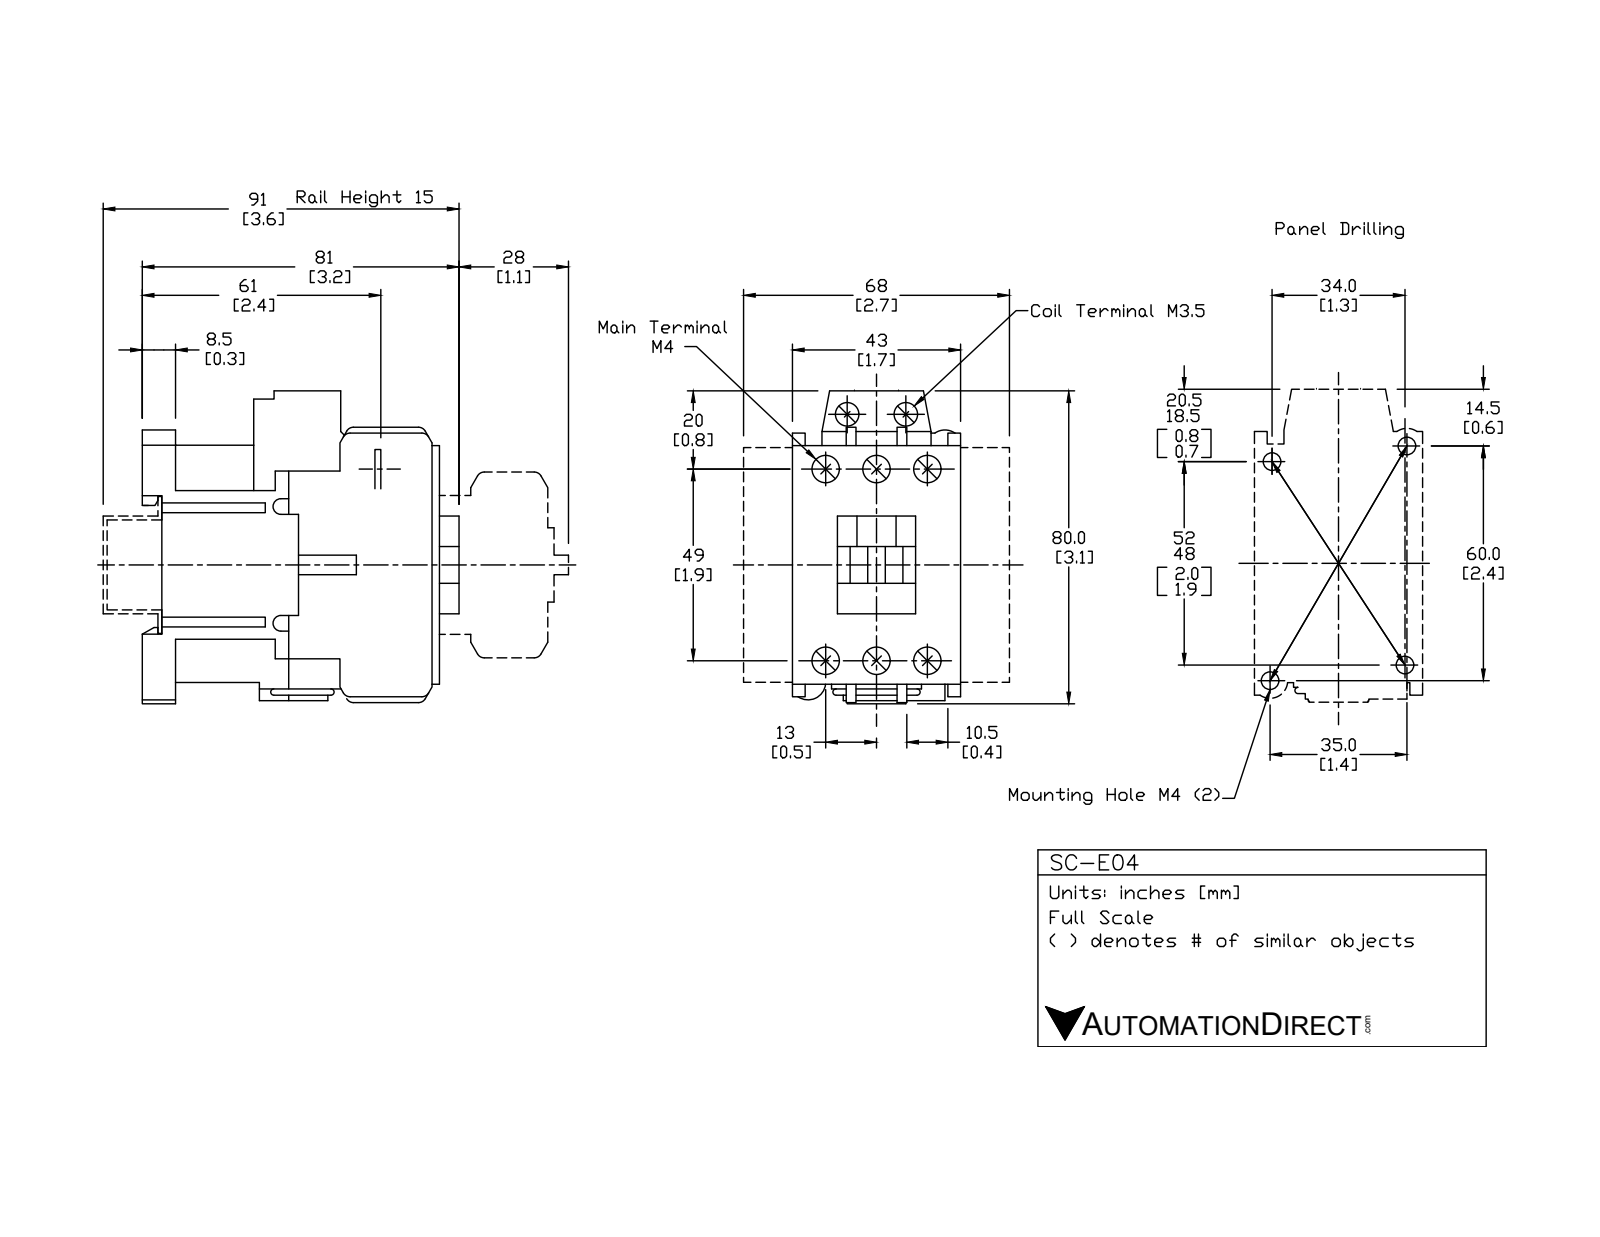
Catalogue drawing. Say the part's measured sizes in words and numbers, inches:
The part is named "SC-E04-440VAC". Its 3-D file was written by "SolidWorks 2015 (AUTOMOTIVE_DESIGN)". It is 1 solid with 1388 faces: 1148 planar, 192 cylindrical and 48 other. Overall it measures 3.189 by 3.189 by 1.693 inches. Its volume is 9.981 cubic inches and its surface area 65.66 square inches. Round holes: 6 of diameter 0.161, 6 of diameter 0.276, 2 of diameter 0.142, 2 of diameter 0.177, 2 of diameter 0.264, 1 of diameter 0.063. Round bosses or shafts: 6 of diameter 0.299, 6 of diameter 0.157, 2 of diameter 0.28, 2 of diameter 0.26, 2 of diameter 0.138. Partial cylindrical surfaces (rounded edges, fillets, slot ends): 32 of radius 0.059, 14 of radius 0.079, 10 of radius 0.02, 4 of radius 0.024, 4 of radius 0.089, 4 of radius 0.14, 2 of radius 0.163, 2 of radius 0.177. The main face-to-face distances are 1.693, 0.512, 0.413, 0.098, 0.925, 1.299, 0.64, 1.053, 0.61, 0.541. The hole center spacings are 0.512, 1.996, 1.929, 0.28, 0.301, 0.592, 0.625, 0.709.
